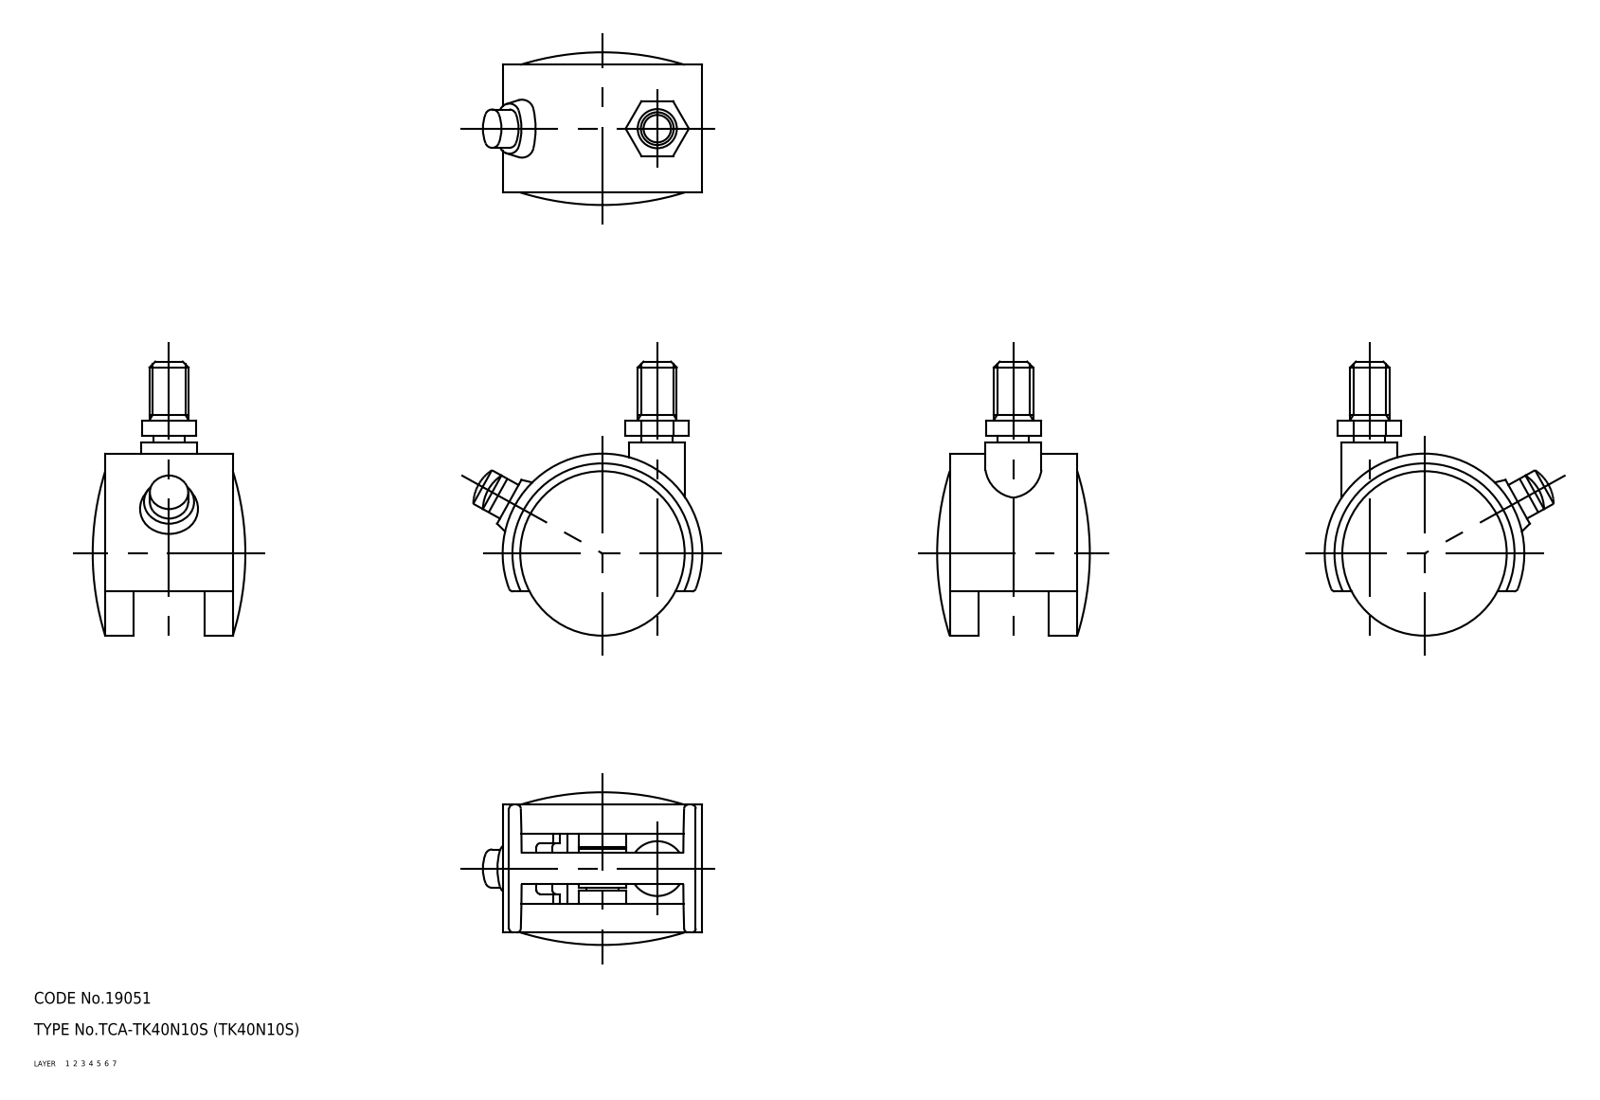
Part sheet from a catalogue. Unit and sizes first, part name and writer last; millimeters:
Units: millimetres
Overall size (bounding box): 70 × 56.05 × 39
Volume: 41 189 mm³ · Surface area: 22 185 mm²
Bodies: 4 solids, 124 faces (0 planar, 0 cylindrical, 124 other)
Part name (STEP PRODUCT): wheel; main shaft; TK40N10S_3971_36
STEP written by: CADfix (AUTOMOTIVE_DESIGN)
